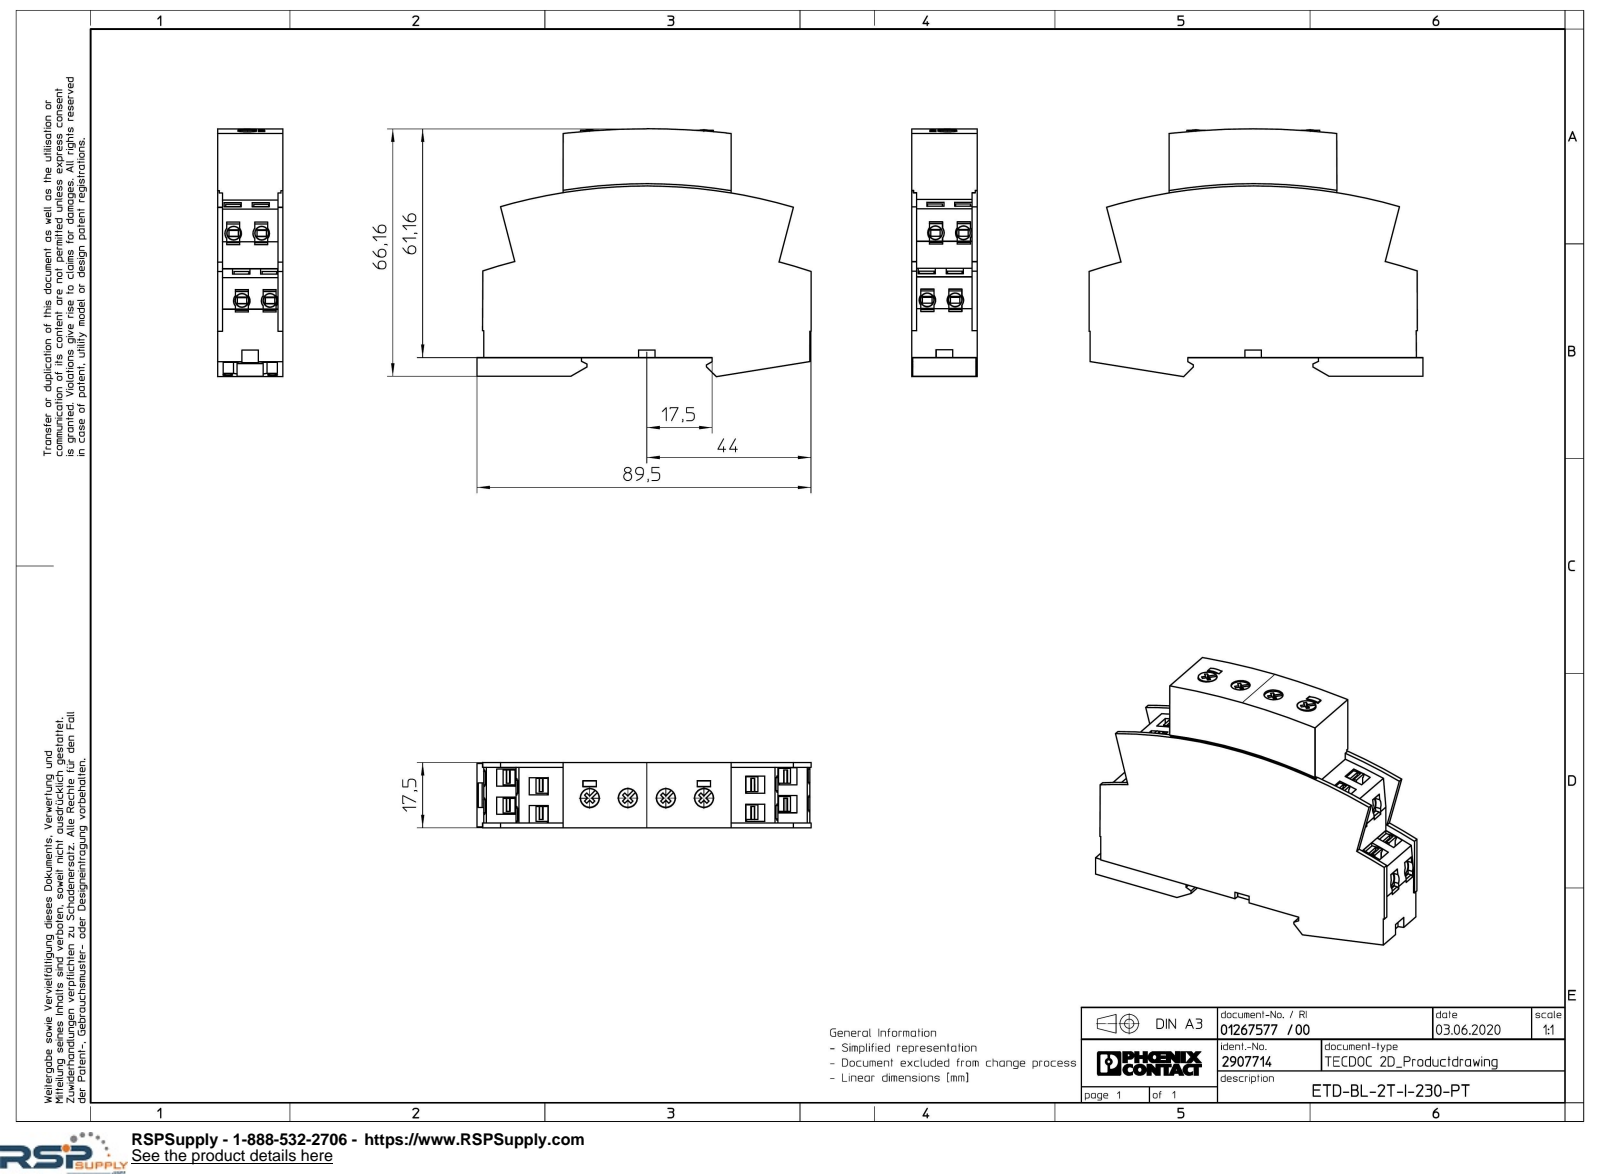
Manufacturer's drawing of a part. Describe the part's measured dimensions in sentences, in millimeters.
The part is named "ETD-BL-2T-I-230-PT-select". Its 3-D file was written by "Creo Elements/Direct Modeling 20.1A 29-Sep-2018 (C) Parametric Technology GmbH (AUTOMOTIVE_DESIGN)". It is 1 solid with 604 faces: 473 planar, 95 cylindrical and 36 other. Overall it measures 89.5 by 66.27 by 17.5 millimeters. Its volume is 74 499 cubic millimeters and its surface area 17 560 square millimeters. Round holes: 4 of diameter 5.1, 3 of diameter 2.5, 2 of diameter 2.6. Round bosses or shafts: 4 of diameter 5. Partial cylindrical surfaces (rounded edges, fillets, slot ends): 9 of radius 0.3, 9 of radius 0.5, 8 of radius 2.2, 4 of radius 0.8, 3 of radius 140, 2 of radius 0.4, 2 of radius 6.25, 2 of radius 138.2. The main face-to-face distances are 17.5, 5, 1.3, 1, 16.2, 15.9, 17.2, 87.4, 17.95, 14.9. The hole center spacings are 10.2, 5, 20.4, 3.37, 3.46, 4.19, 7.6, 8.59.
